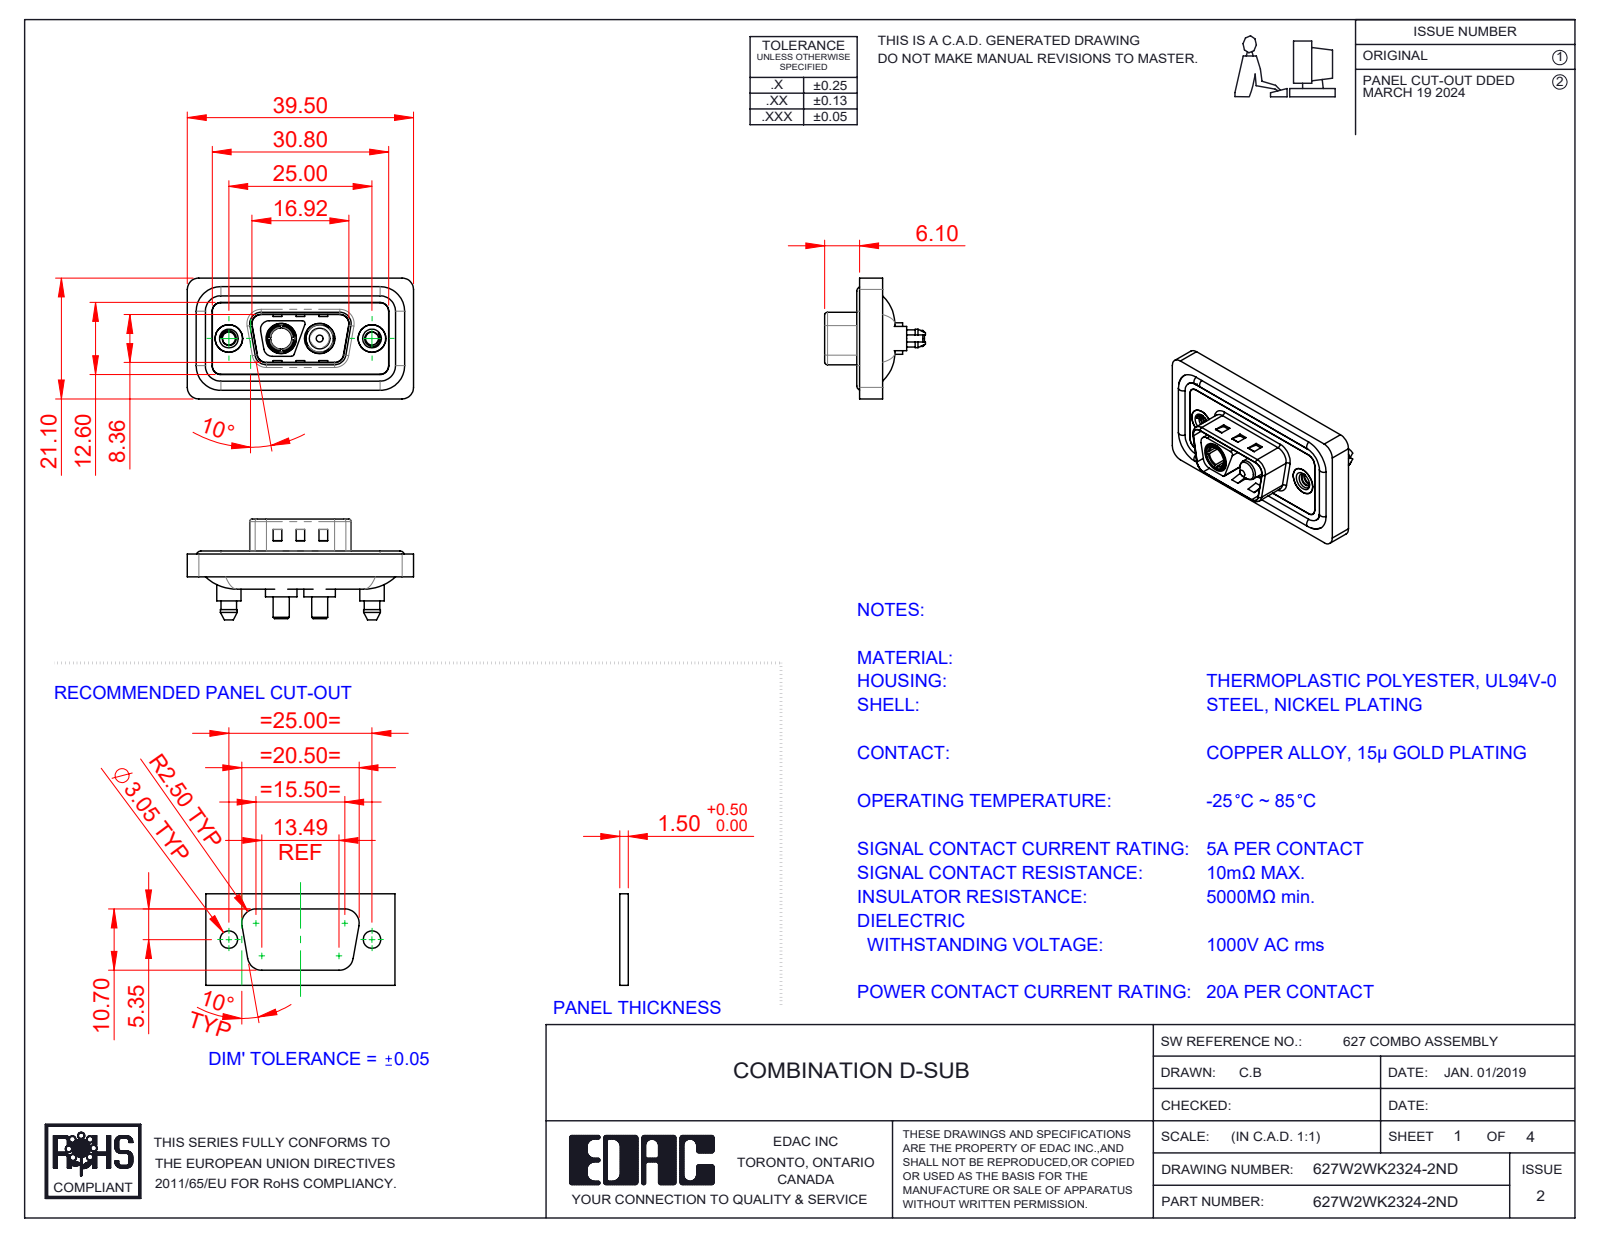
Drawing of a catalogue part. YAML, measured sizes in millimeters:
part_name: "Power Socket_20A S; 627Combo Threaded Boardlock_5; 627Combo Threaded Boardlock_D; Power Pin_20A S (+5 more)"
step_written_by: "SolidWorks 2023 (CONFIG_CONTROL_DESIGN)"
units: millimeters
bodies: {solids: 11, faces: 592, planar: 205, cylindrical: 267, other: 120}
overall_size: [39.5, 21.1, 17.6]
volume: 4689
surface_area: 7678
round_holes:
  - {diameter: 2.26, count: 2}
  - {diameter: 4, count: 2}
  - {diameter: 4.8, count: 2}
  - {diameter: 4.85, count: 2}
  - {diameter: 5, count: 2}
  - {diameter: 5.3, count: 2}
  - {diameter: 3.7, count: 1}
round_bosses_or_shafts:
  - {diameter: 1.6, count: 4}
  - {diameter: 5.5, count: 2}
  - {diameter: 5.4, count: 2}
  - {diameter: 5.2, count: 2}
  - {diameter: 4.9, count: 2}
  - {diameter: 4.75, count: 2}
  - {diameter: 4.25, count: 2}
  - {diameter: 3.75, count: 2}
partial_cylinders:
  - {radius: 1.5, count: 26}
  - {radius: 2, count: 18}
  - {radius: 0.5, count: 10}
  - {radius: 1.6, count: 10}
  - {radius: 0.25, count: 4}
  - {radius: 0.6, count: 4}
  - {radius: 0.65, count: 4}
  - {radius: 0.9, count: 4}
face_to_face_distances: [0.4, 1.1, 2.9, 3.1, 0.5, 1.6, 1.5, 4, 1.8, 3.2]
hole_center_spacings: [9.14, 15.86, 6.72, 25]
